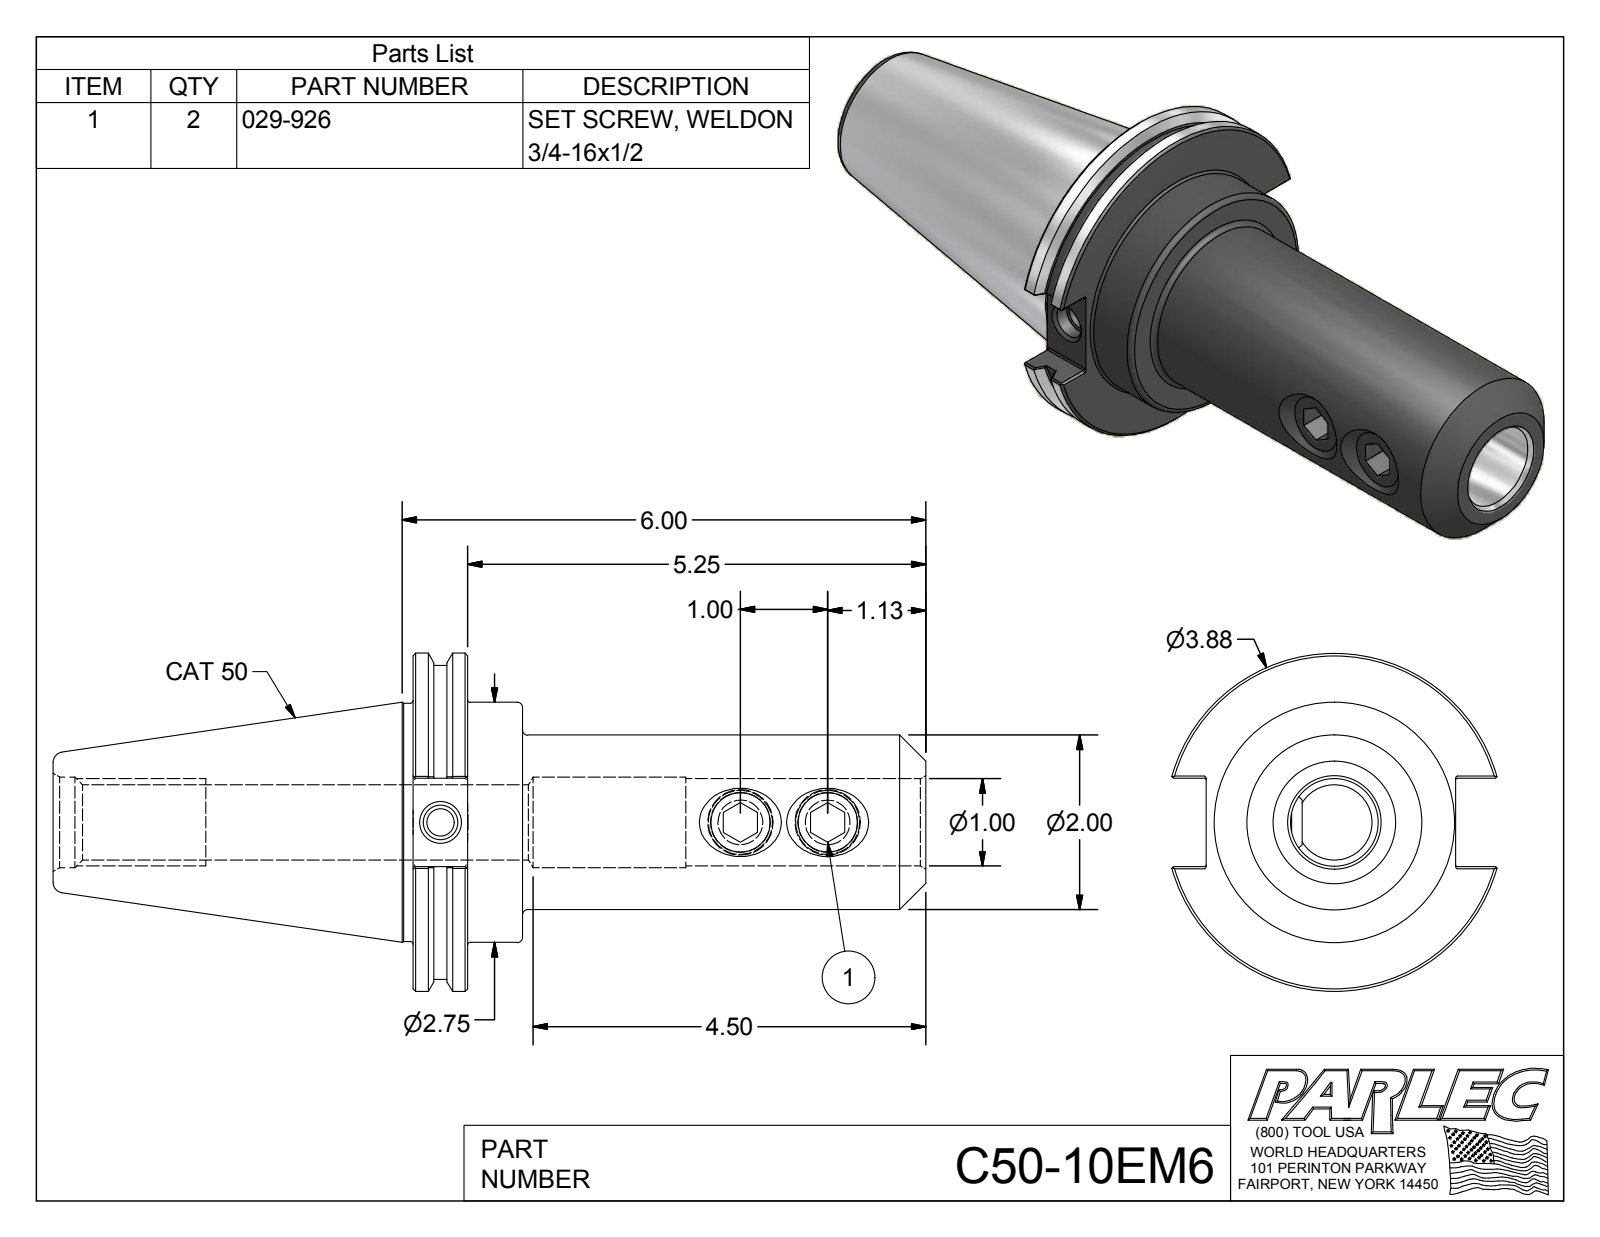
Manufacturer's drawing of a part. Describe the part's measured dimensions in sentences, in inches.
The part is named "C50-10EM6; C50-10EM6-1; 029-926". Its 3-D file was written by "Autodesk Inventor 2012 (AUTOMOTIVE_DESIGN)". It is 3 solids with 118 faces: 51 planar, 31 cylindrical and 36 other. Overall it measures 10 by 3.875 by 3.729 inches. Its volume is 33.16 cubic inches and its surface area 122.7 square inches. Round holes: 2 of diameter 0.682, 1 of diameter 0.315, 1 of diameter 0.399, 1 of diameter 0.865, 1 of diameter 1, 1 of diameter 1.038, 1 of diameter 1.04. Round bosses or shafts: 2 of diameter 0.75, 1 of diameter 3.875, 1 of diameter 3.594, 1 of diameter 2.75, 1 of diameter 2.73, 1 of diameter 2. Partial cylindrical surfaces (rounded edges, fillets, slot ends): 12 of radius 0.02. The main face-to-face distances are 0.625, 1.255, 0.63, 0.5, 0.394, 5.875, 5.25, 4.62, 2.259, 4.125. The hole center spacings are 1, 3.435, 4.435.
